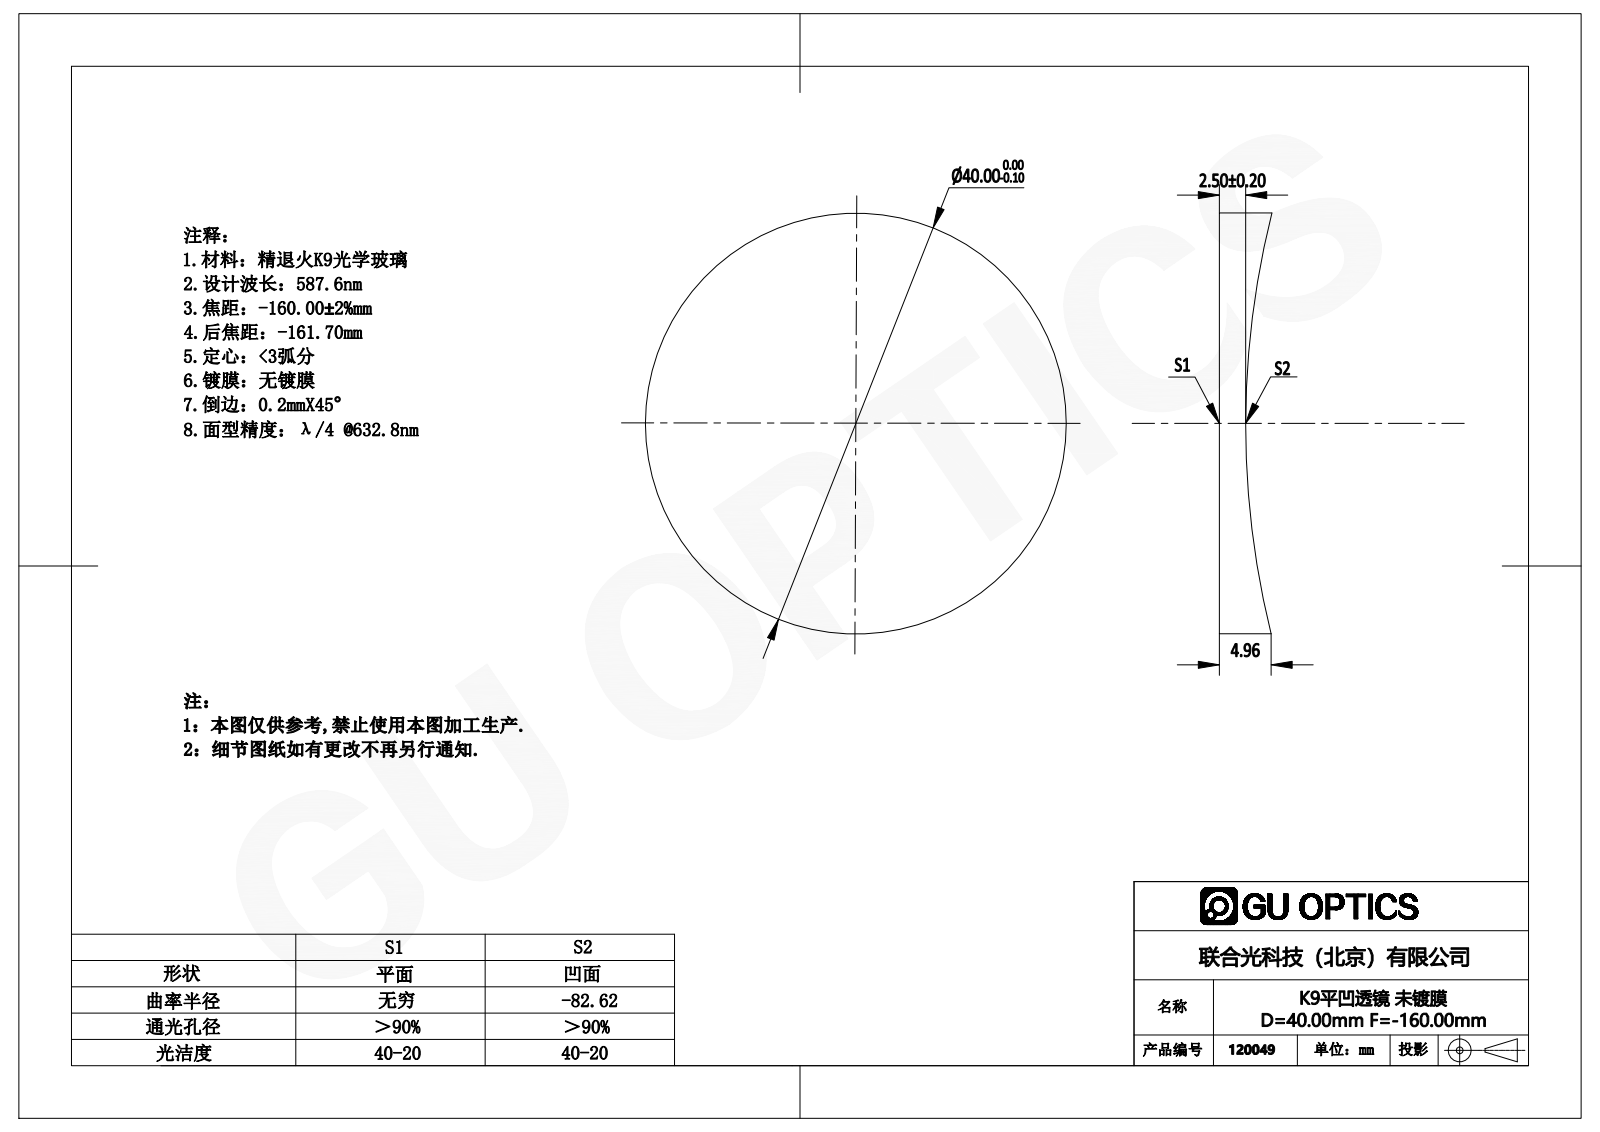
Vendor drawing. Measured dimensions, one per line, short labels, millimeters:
name: 120049
written by: SolidWorks 2016 (AUTOMOTIVE_DESIGN)
unit: mm
bodies: 1 solid, 5 faces (1 planar, 2 cylindrical, 2 other)
size: 40 × 40 × 5
volume: 4 710 mm³; area: 3 160 mm²
bosses: 1× ⌀40
